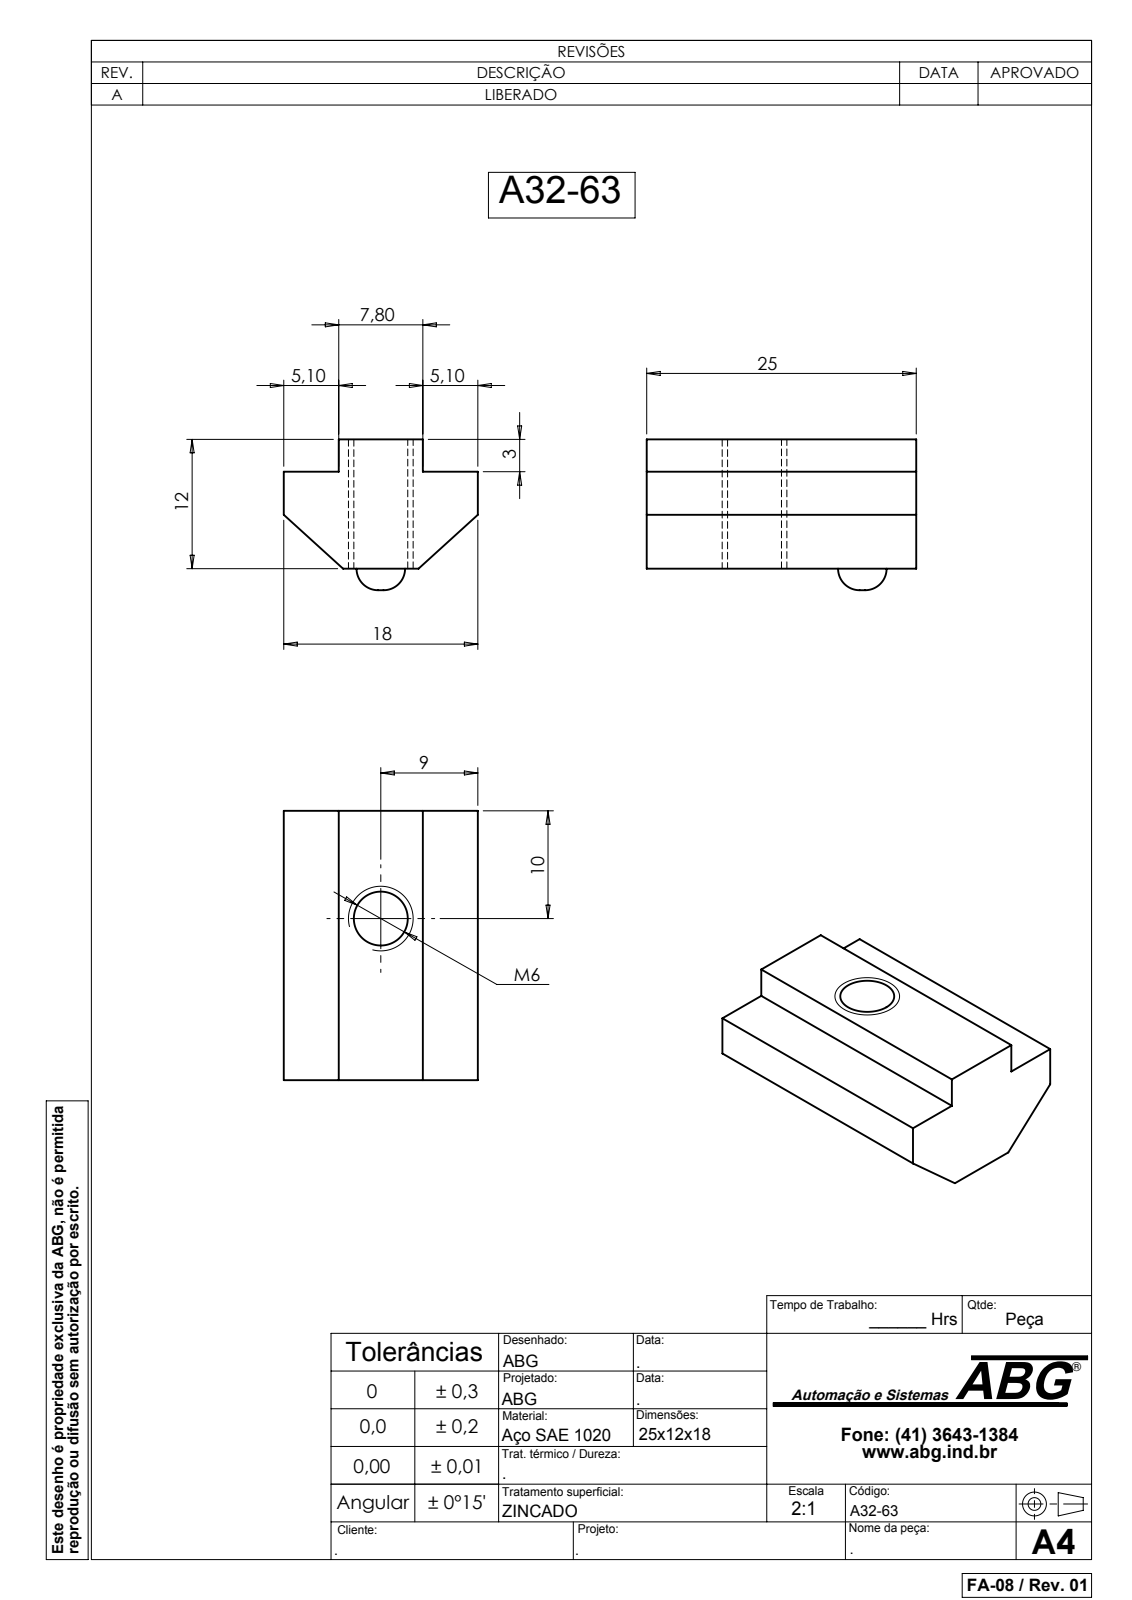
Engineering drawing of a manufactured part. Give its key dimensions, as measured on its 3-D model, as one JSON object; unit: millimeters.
{"part_name": "A32-63", "step_written_by": "SolidWorks 2007 (CONFIG_CONTROL_DESIGN)", "units": "millimeters", "bodies": {"solids": 1, "faces": 17, "planar": 13, "cylindrical": 2, "other": 2}, "overall_size": [25, 18, 14], "volume_mm3": 3734, "surface_area_mm2": 1826, "round_holes": [[5, 1]], "face_to_face_distances": [3, 25, 5.1, 12.9, 9, 12, 18, 7.8, 2, 11]}
